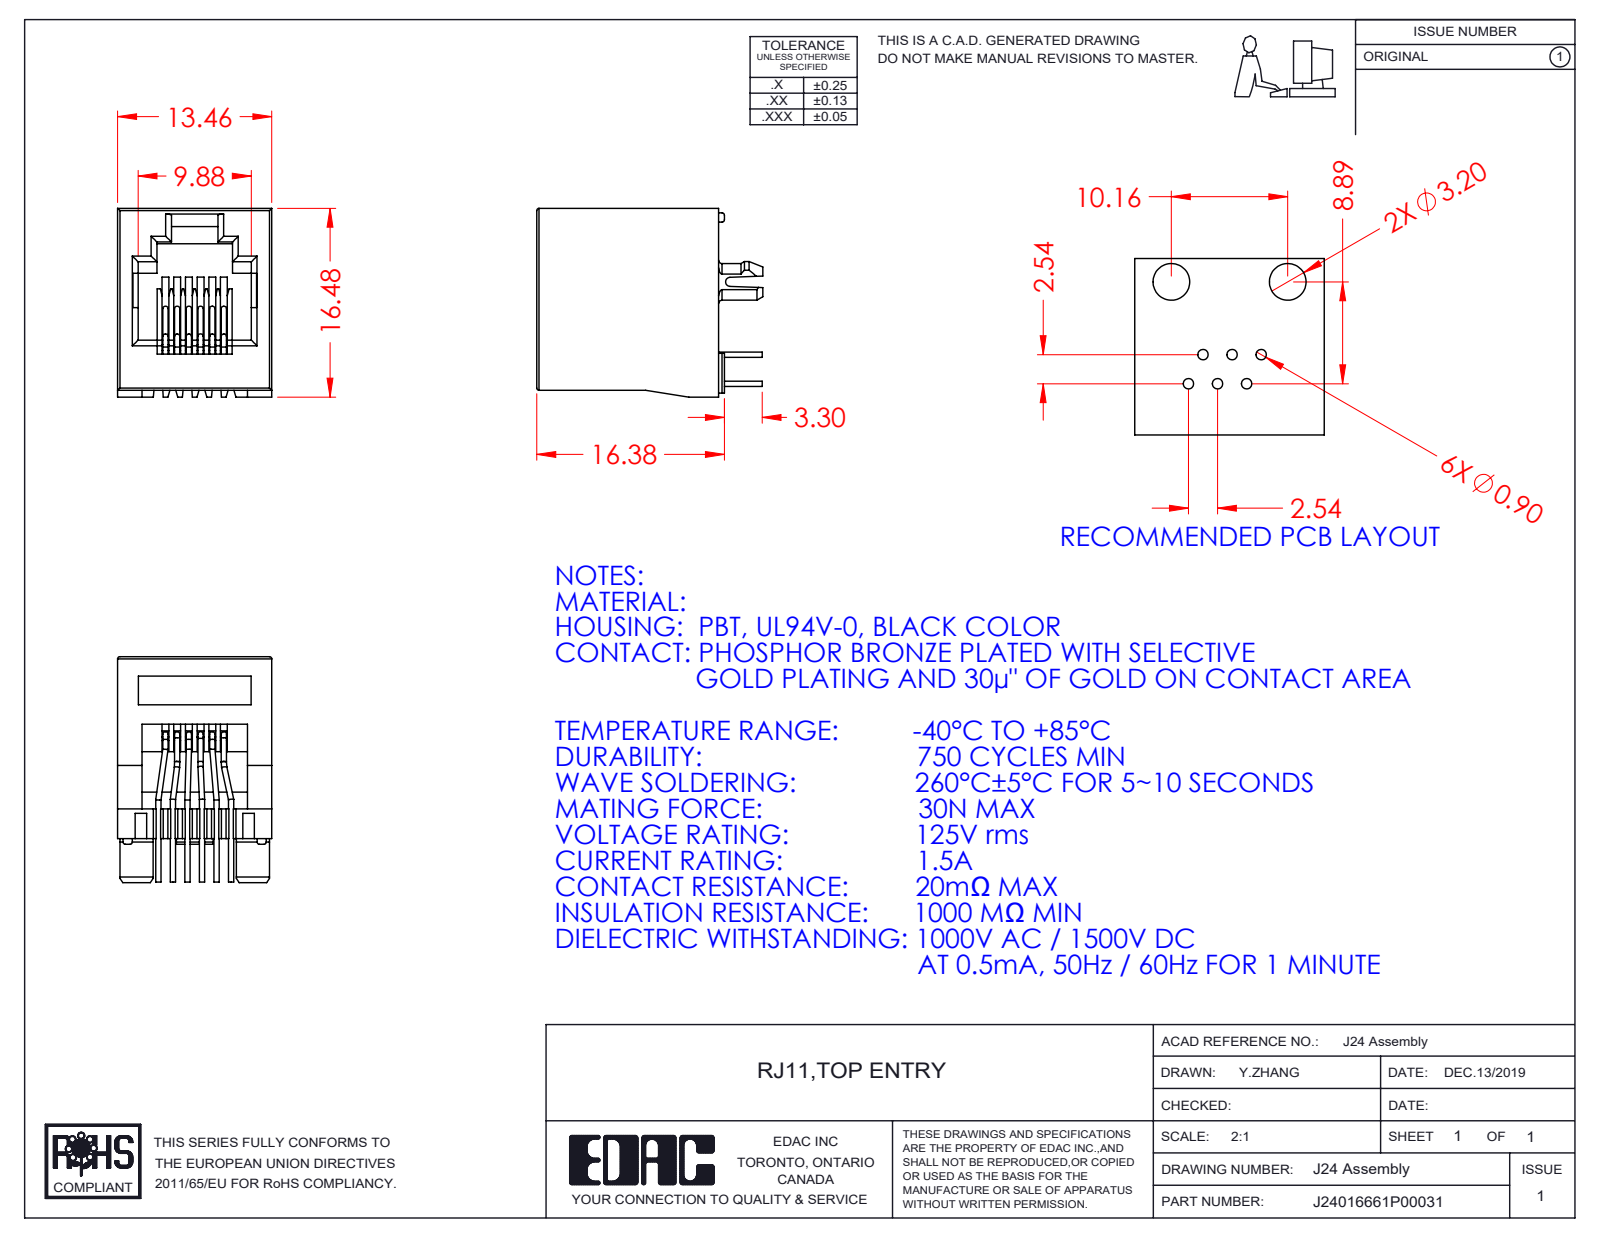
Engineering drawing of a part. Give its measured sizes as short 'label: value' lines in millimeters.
name: 24 Insulator_Standard; RJ24016661P00031; 24 Contacts_Standard
written by: SolidWorks 2016 (CONFIG_CONTROL_DESIGN)
unit: mm
bodies: 7 solids, 444 faces (256 planar, 150 cylindrical, 38 other)
size: 19.73 × 16.48 × 13.46
volume: 1 745 mm³; area: 2 930 mm²
holes: 6× ⌀0.46, 2× ⌀2.1
bosses: 26× ⌀0.46
rounds: 16× R0.5, 10× R0.2, 6× R0.32, 6× R0.34, 3× R0.25, 2× R1.6, 2× R1.77, 1× R0.4
face distances: 13.46, 1.02, 1.79, 11.67, 0.6, 15.87, 8.24, 3.43, 10.03, 1.64
hole spacings: 2.84, 2.54, 4.58, 5.08, 13.1, 6.84, 10.16, 10.35
